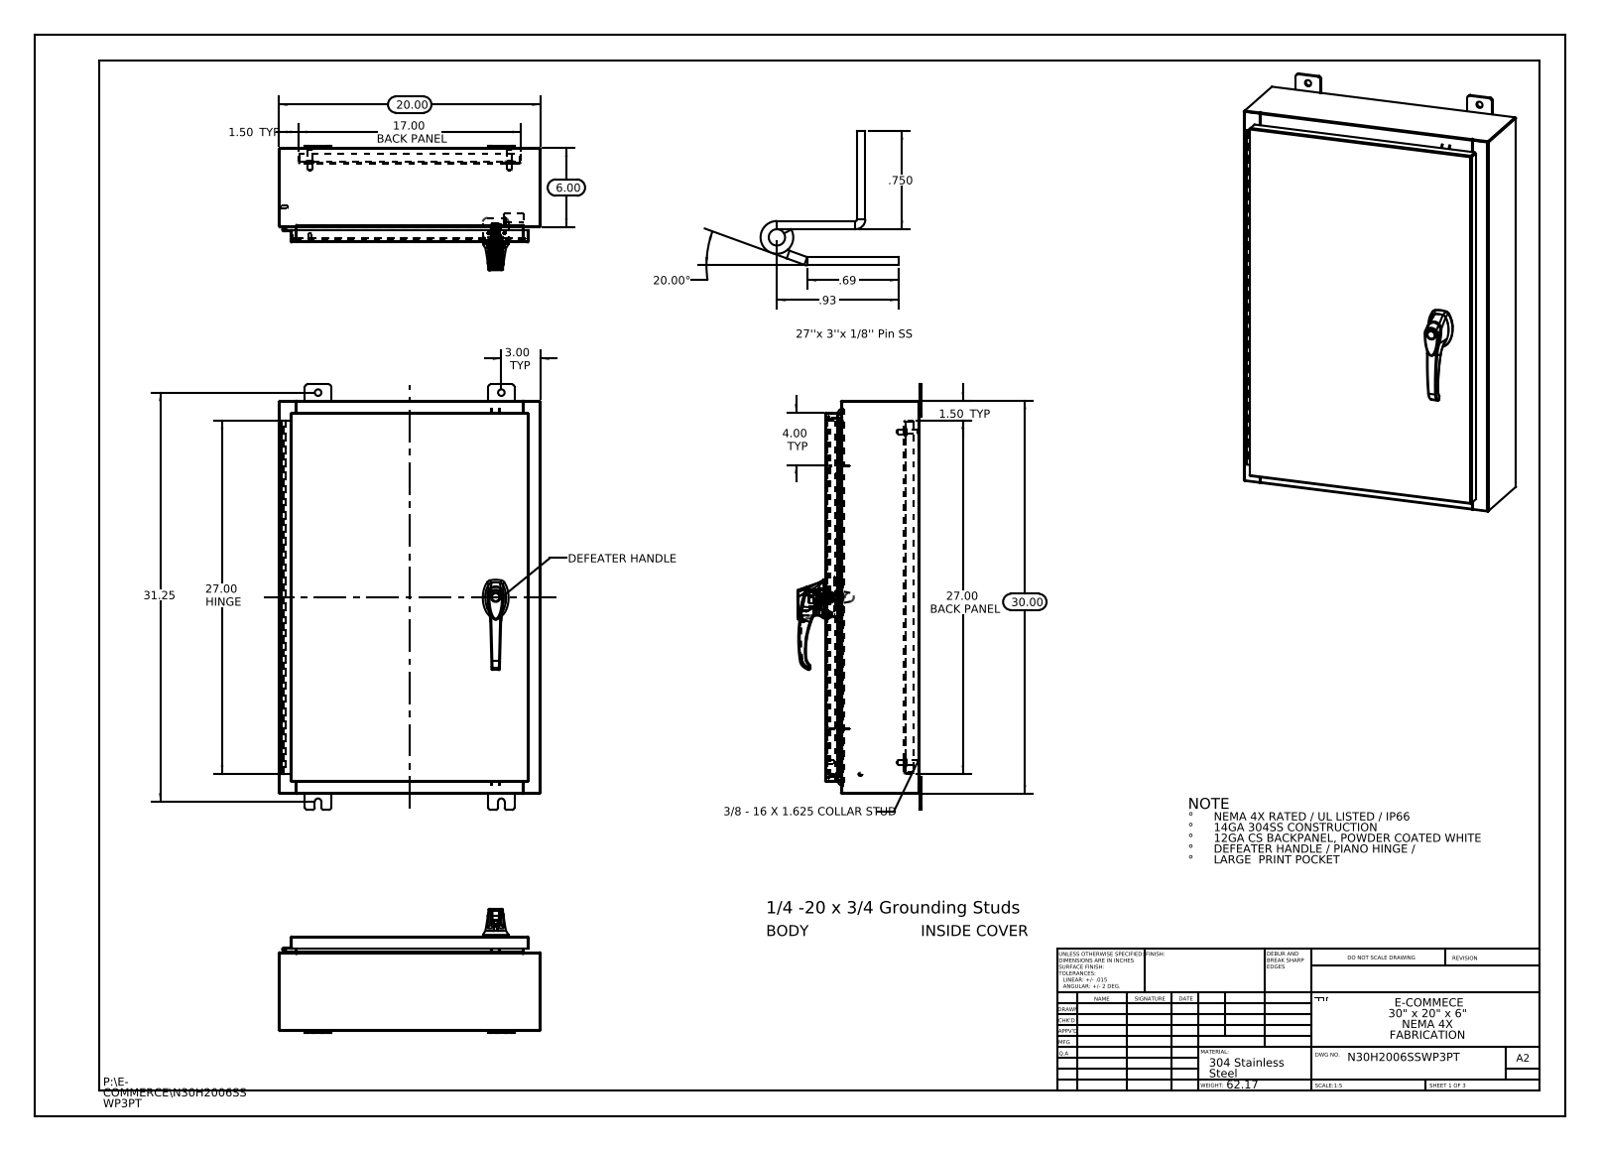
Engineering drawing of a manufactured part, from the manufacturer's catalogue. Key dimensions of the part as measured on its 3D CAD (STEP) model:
Part name (STEP PRODUCT): g26103103_26163303; N30H2006SSWP3PT Defeater Handle Rod; 00005090; 10_30 CD Stud (+8 more)
STEP written by: SolidWorks 2013 (CONFIG_CONTROL_DESIGN)
Units: inches
Bodies: 37 solids, 2662 faces (971 planar, 993 cylindrical, 698 other)
Overall size (bounding box): 32.5 × 20 × 9.495
Volume: 221.6 in³ · Surface area: 5 445 in²
Round holes (diameter × count): ⌀0.5 ×8, ⌀0.25 ×4, ⌀0.138 ×3, ⌀0.161 ×3, ⌀0.079 ×2, ⌀0.203 ×2, ⌀0.313 ×2, ⌀0.437 ×2, ⌀0.125 ×1, ⌀0.125 ×1, ⌀0.197 ×1, ⌀0.276 ×1
Round bosses / shafts (diameter × count): ⌀0.625 ×4, ⌀0.375 ×4, ⌀0.33 ×4, ⌀0.157 ×4, ⌀0.14 ×4, ⌀0.315 ×3, ⌀0.236 ×3, ⌀1.181 ×1
Partial cylindrical surfaces — rounded edges, fillets, slot ends (radius × count): R0.118 ×37, R0.006 ×33, R0.013 ×24, R0.19 ×24, R0.088 ×18, R0.039 ×15, R0.028 ×12, R0.008 ×6
Main face-to-face distances: 0.075, 7.126, 0.104, 7.051, 7.201, 1, 1.075, 6.051, 6.126, 1.179
Hole centre spacings: 8.369, 15.143, 0.295, 0.625, 0.841, 1.25, 1.313, 1.561
